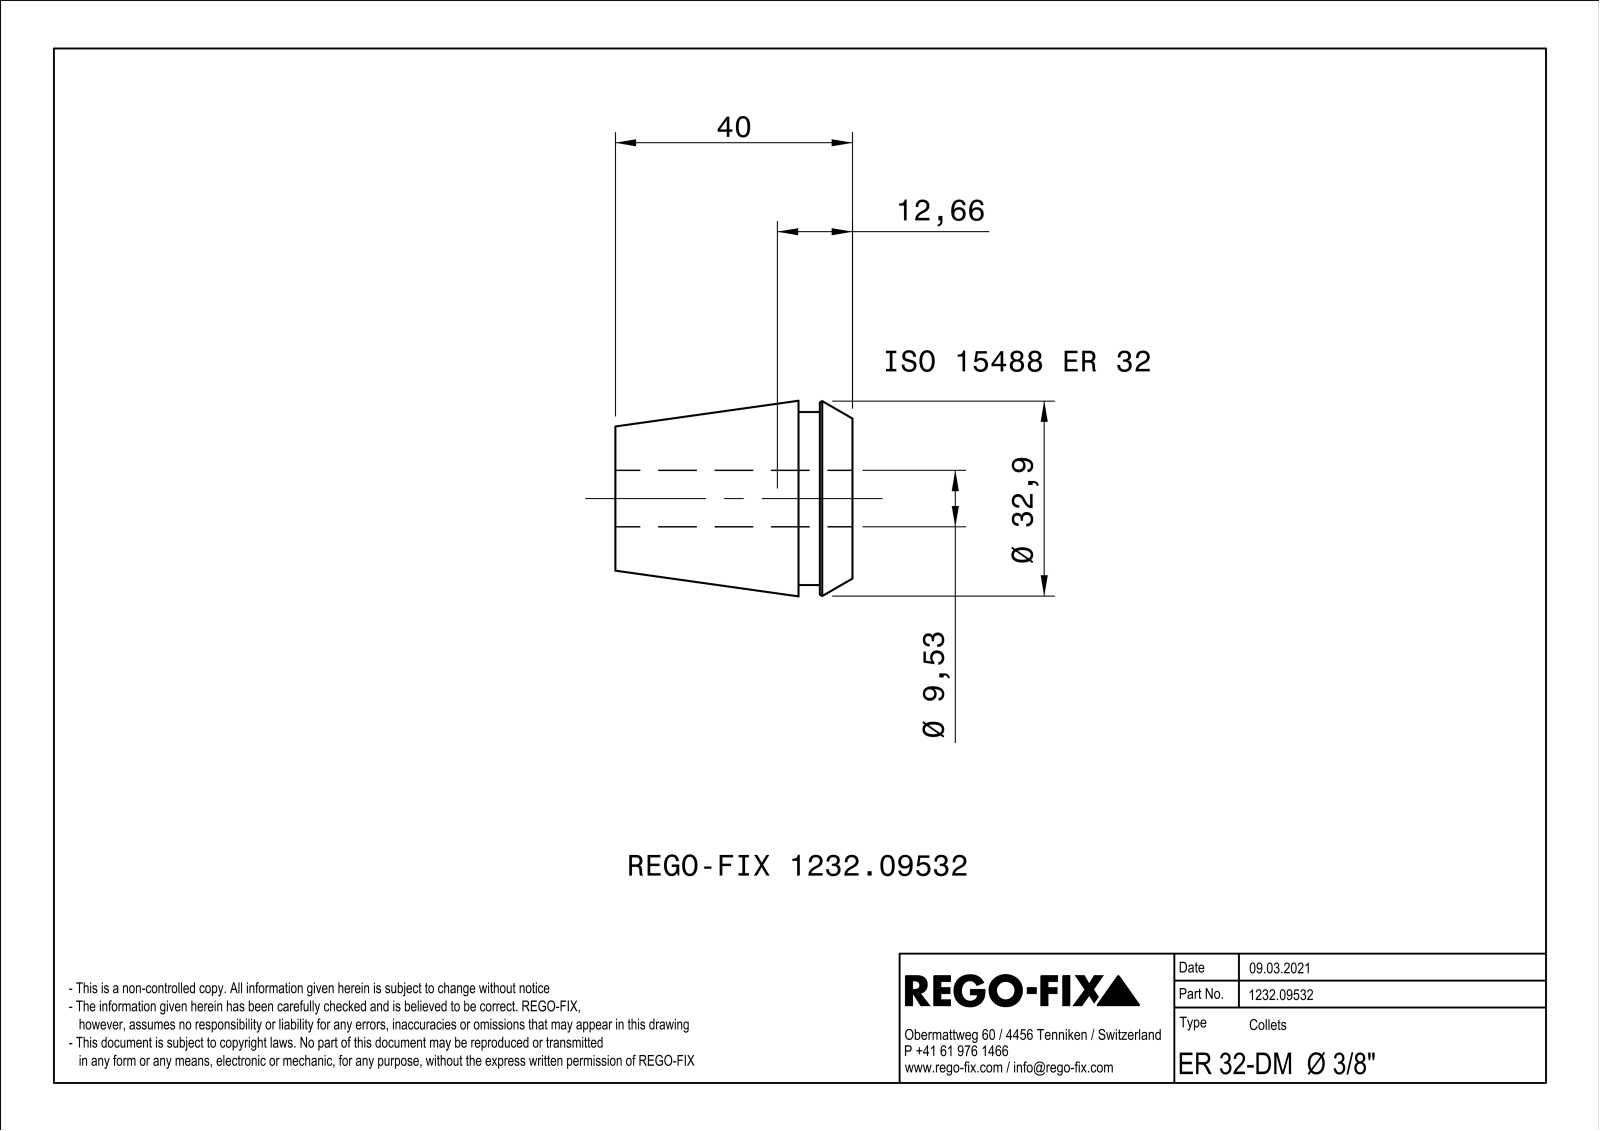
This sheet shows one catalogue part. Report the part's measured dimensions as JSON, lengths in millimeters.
{"part_name": "NOCUT", "step_written_by": "SIEMENS PLM Software Solid Edge ST10 (AUTOMOTIVE_DESIGN)", "units": "millimeters", "bodies": {"solids": 1, "faces": 154, "planar": 80, "cylindrical": 9, "other": 65}, "overall_size": [40, 32.98, 32.98], "volume_mm3": 19042, "surface_area_mm2": 14273, "round_holes": [[9.53, 1]], "round_bosses_or_shafts": [[29.2, 1]], "face_to_face_distances": [1, 40, 9.1, 30.9, 5.5, 3.6, 34.5, 16, 10.5, 6.9]}
